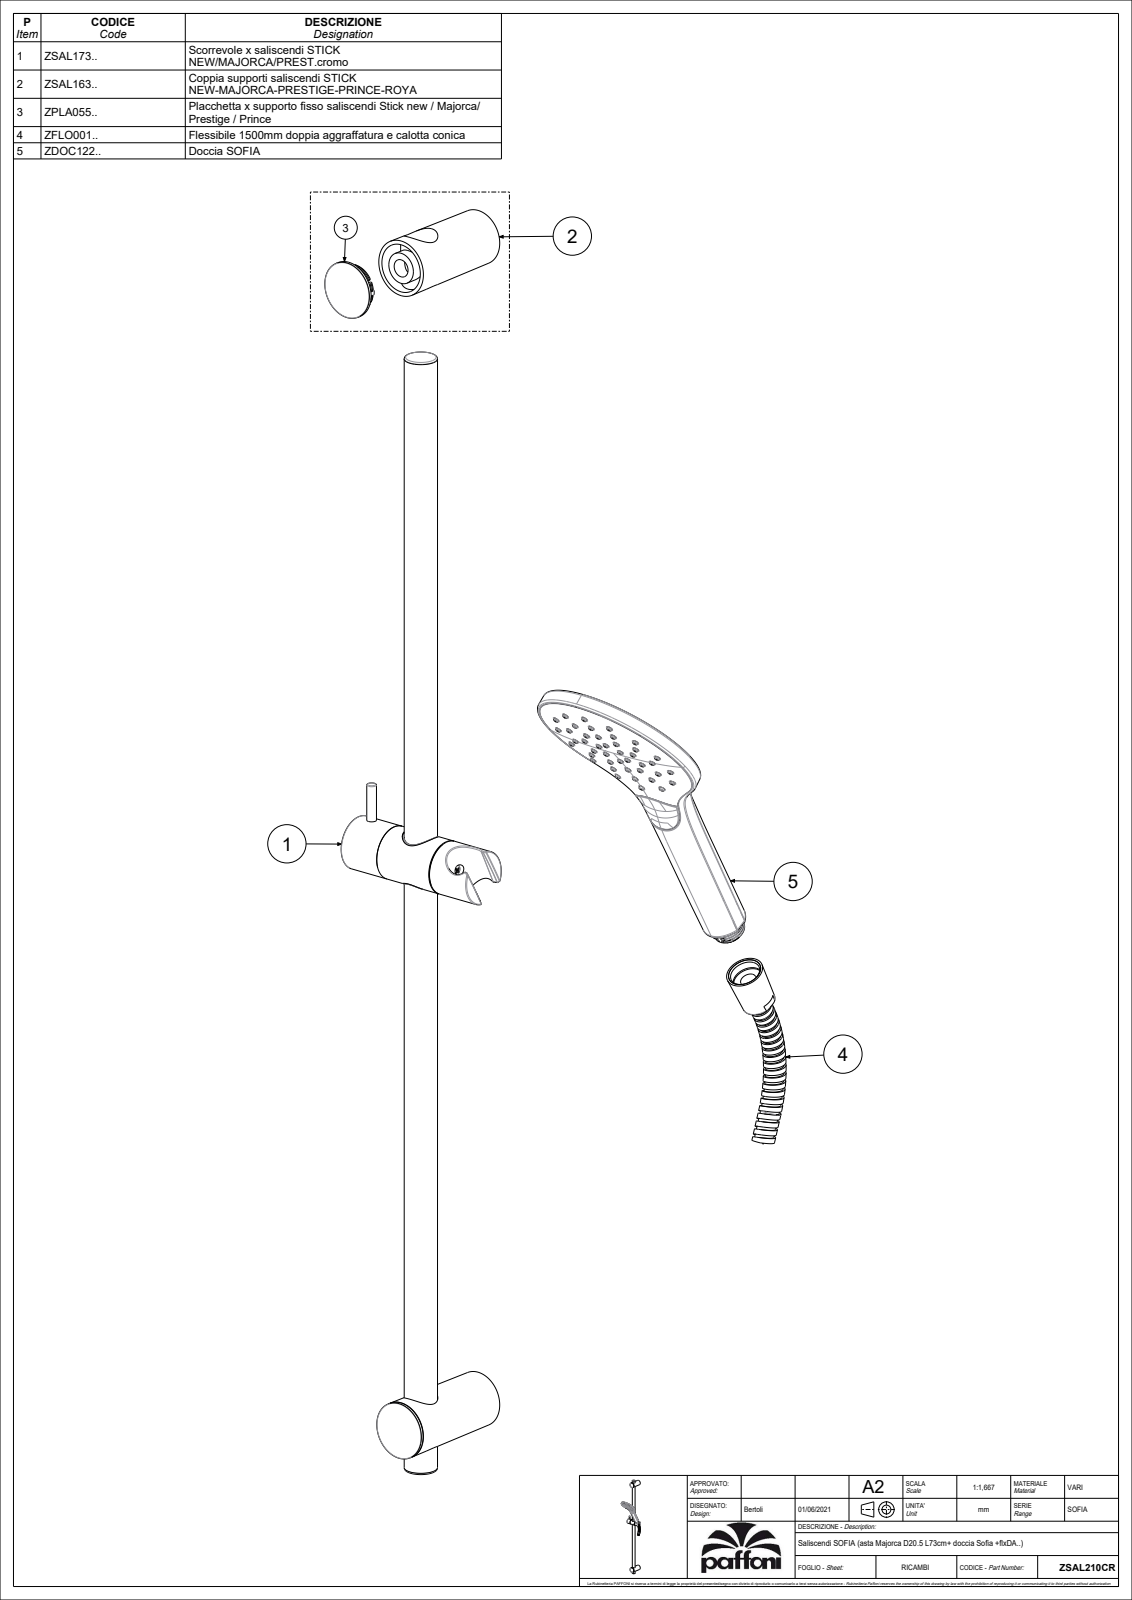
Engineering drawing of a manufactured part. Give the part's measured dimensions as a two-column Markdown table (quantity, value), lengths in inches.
| quantity | value |
| --- | --- |
| part name | M50520-020_3; M50330-013_1; M50520-011_1; M50520-012_1 (+8 more) |
| STEP written by | CREO PARAMETRIC BY PTC INC, 2020044 (CONFIG_CONTROL_DESIGN) |
| units | inches |
| bodies | 35 solids, 3958 faces (1050 planar, 832 cylindrical, 2076 other) |
| overall size | 28.898 × 8.276 × 5.79 |
| volume | 12.19 in³ |
| surface area | 477.2 in² |
| round holes (diameter × count) | 0.157 × 5, 0.236 × 4, 0.118 × 3, 0.213 × 2, 0.394 × 2, 0.433 × 2, 0.441 × 2, 0.827 × 2, 0.886 × 2, 1.063 × 2, 1.22 × 2, 0.028 × 1 |
| round bosses / shafts (diameter × count) | 0.276 × 5, 1.228 × 3, 0.472 × 3, 1.437 × 2, 1.378 × 2, 0.984 × 2, 0.882 × 2, 0.807 × 2 |
| partial cylindrical surfaces (radius × count) | 0.008 × 46, 0.02 × 46, 0.012 × 27, 0.039 × 23, 0.059 × 14, 0.748 × 12, 0.024 × 10, 0.728 × 8 |
| main face-to-face distances | 0.043, 14.43, 14.473, 14.386, 0.098, 2.913, 0.059, 0.079, 0.118, 1.063 |
| hole center spacings | 1.417, 0.627, 0.8, 0.979, 1.473, 1.522, 1.769, 1.89 |
